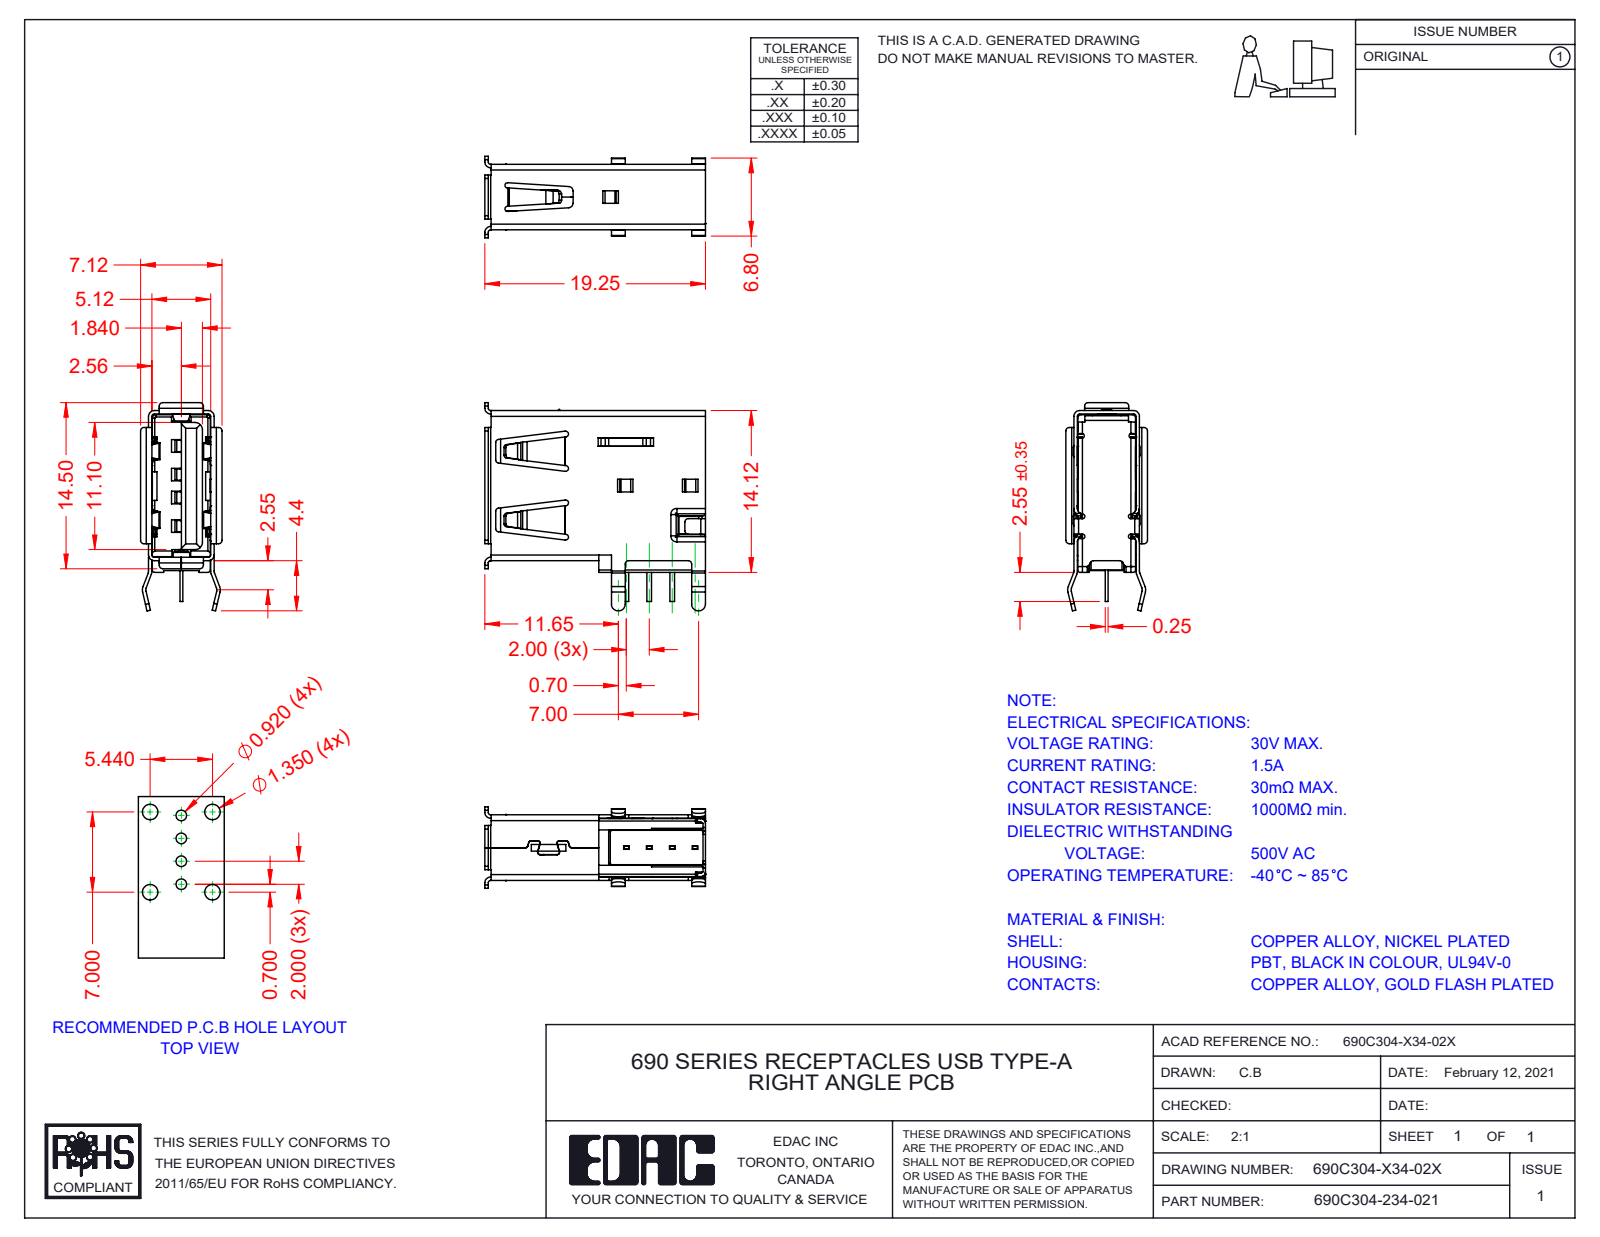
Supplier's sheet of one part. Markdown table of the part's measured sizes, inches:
| quantity | value |
| --- | --- |
| part name | 690C304-634-021; Contact2 690C304-X34-02X; Shell 690C304-X34-02X; Contact3 690C304-X34-02X (+3 more) |
| STEP written by | SolidWorks 2020 (AUTOMOTIVE_DESIGN) |
| units | inches |
| bodies | 6 solids, 1391 faces (890 planar, 426 cylindrical, 75 other) |
| overall size | 0.758 × 0.717 × 0.28 |
| volume | 0.041 in³ |
| surface area | 4.352 in² |
| partial cylindrical surfaces (radius × count) | 0.012 × 59, 0.006 × 38, 0.008 × 35, 0.005 × 24, 0.016 × 23, 0.024 × 22, 0.01 × 20, 0.004 × 15 |
| main face-to-face distances | 0.213, 0.202, 0.225, 0.113, 0.101, 0.04, 0.504, 0.173, 0.05, 0.043 |
